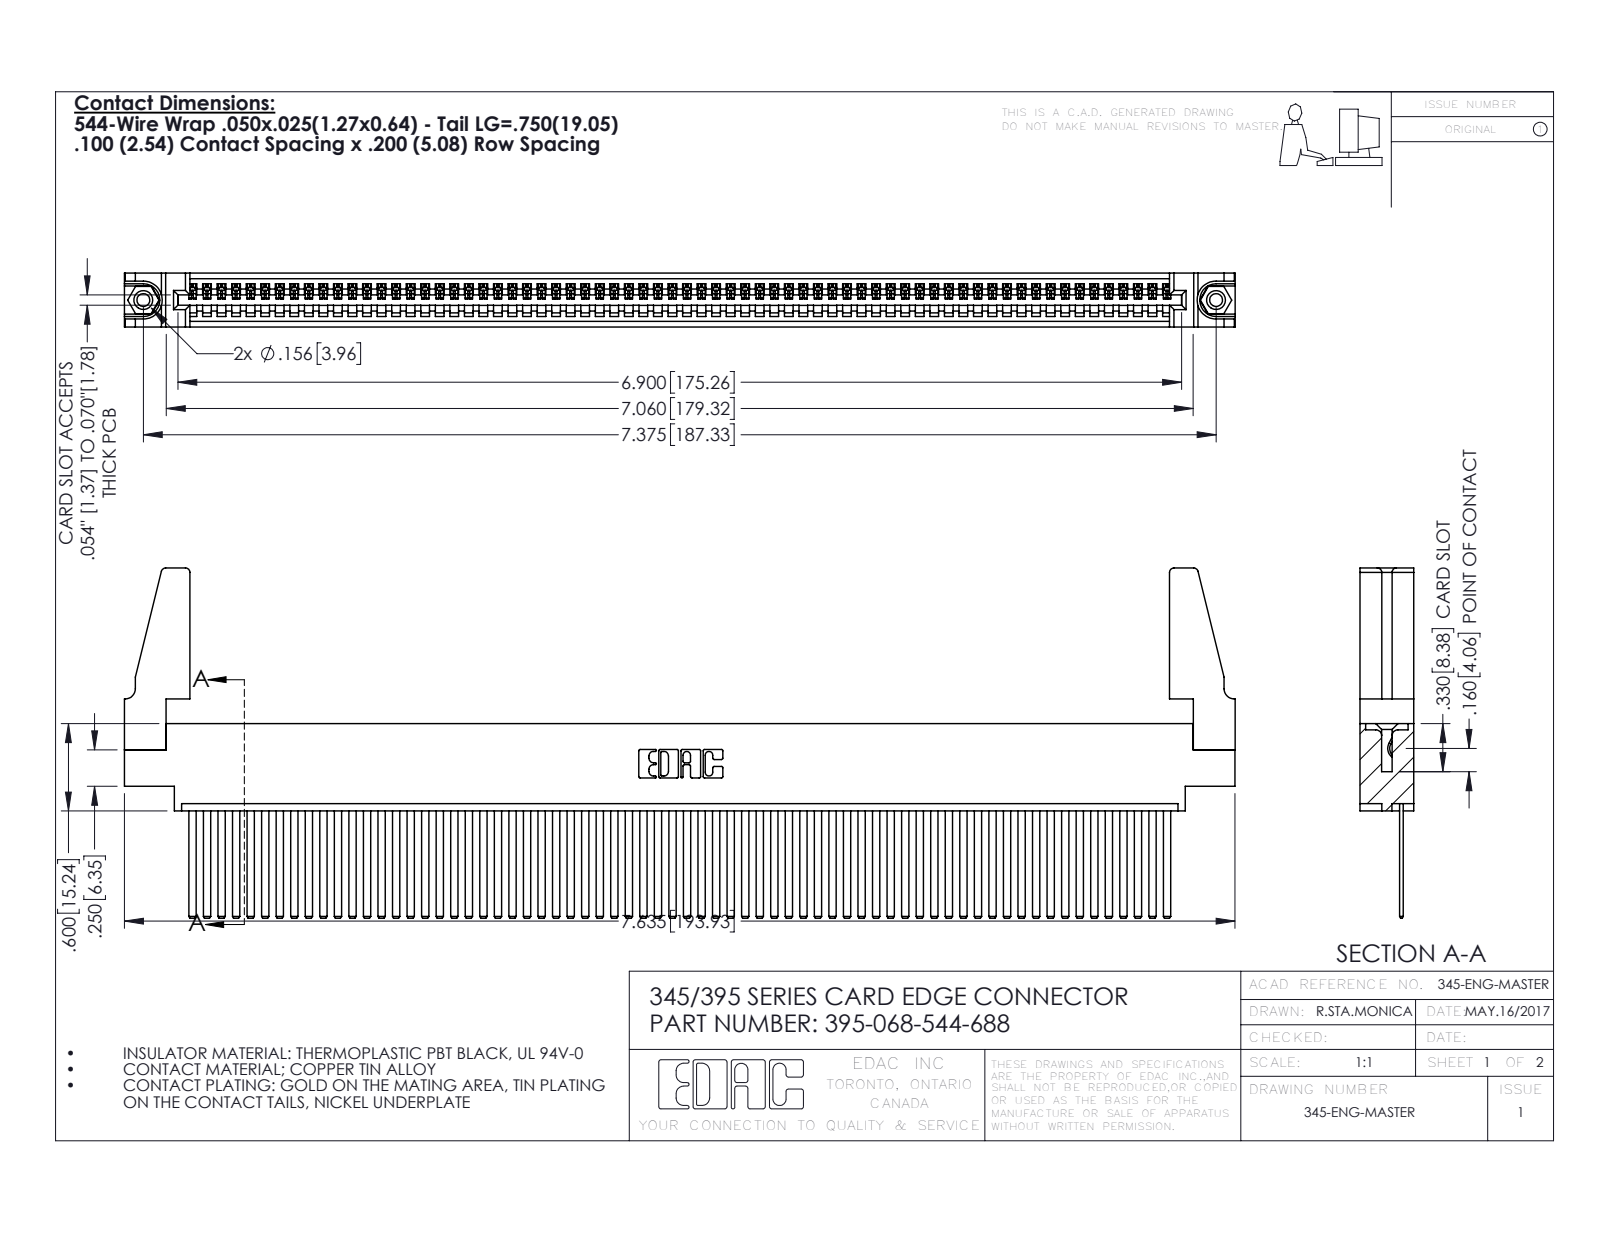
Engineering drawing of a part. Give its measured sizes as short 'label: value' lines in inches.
name: 345-250-001_345-250-001-102; 395-068-544-688; 345-292-001_345-293-144; 345-220-078_345-220-088 (+1 more)
written by: SolidWorks 2016 (CONFIG_CONTROL_DESIGN)
unit: in
bodies: 73 solids, 3790 faces (2604 planar, 1170 cylindrical, 16 other)
size: 7.636 × 2.407 × 0.37
volume: 1.377 in³; area: 49.03 in²
holes: 2× ⌀0.089, 2× ⌀0.125, 2× ⌀0.156, 1× ⌀0.064
bosses: 2× ⌀0.155
rounds: 136× R0.006, 22× R0.01, 8× R0.03, 6× R0.007, 6× R0.031, 3× R0.026, 2× R0.031, 2× R0.04
face distances: 0.072, 0.298, 0.098, 0.272, 0.025, 0.37, 0.2, 0.225, 0.175, 0.149
hole spacings: 0.27, 7.139, 7.375
